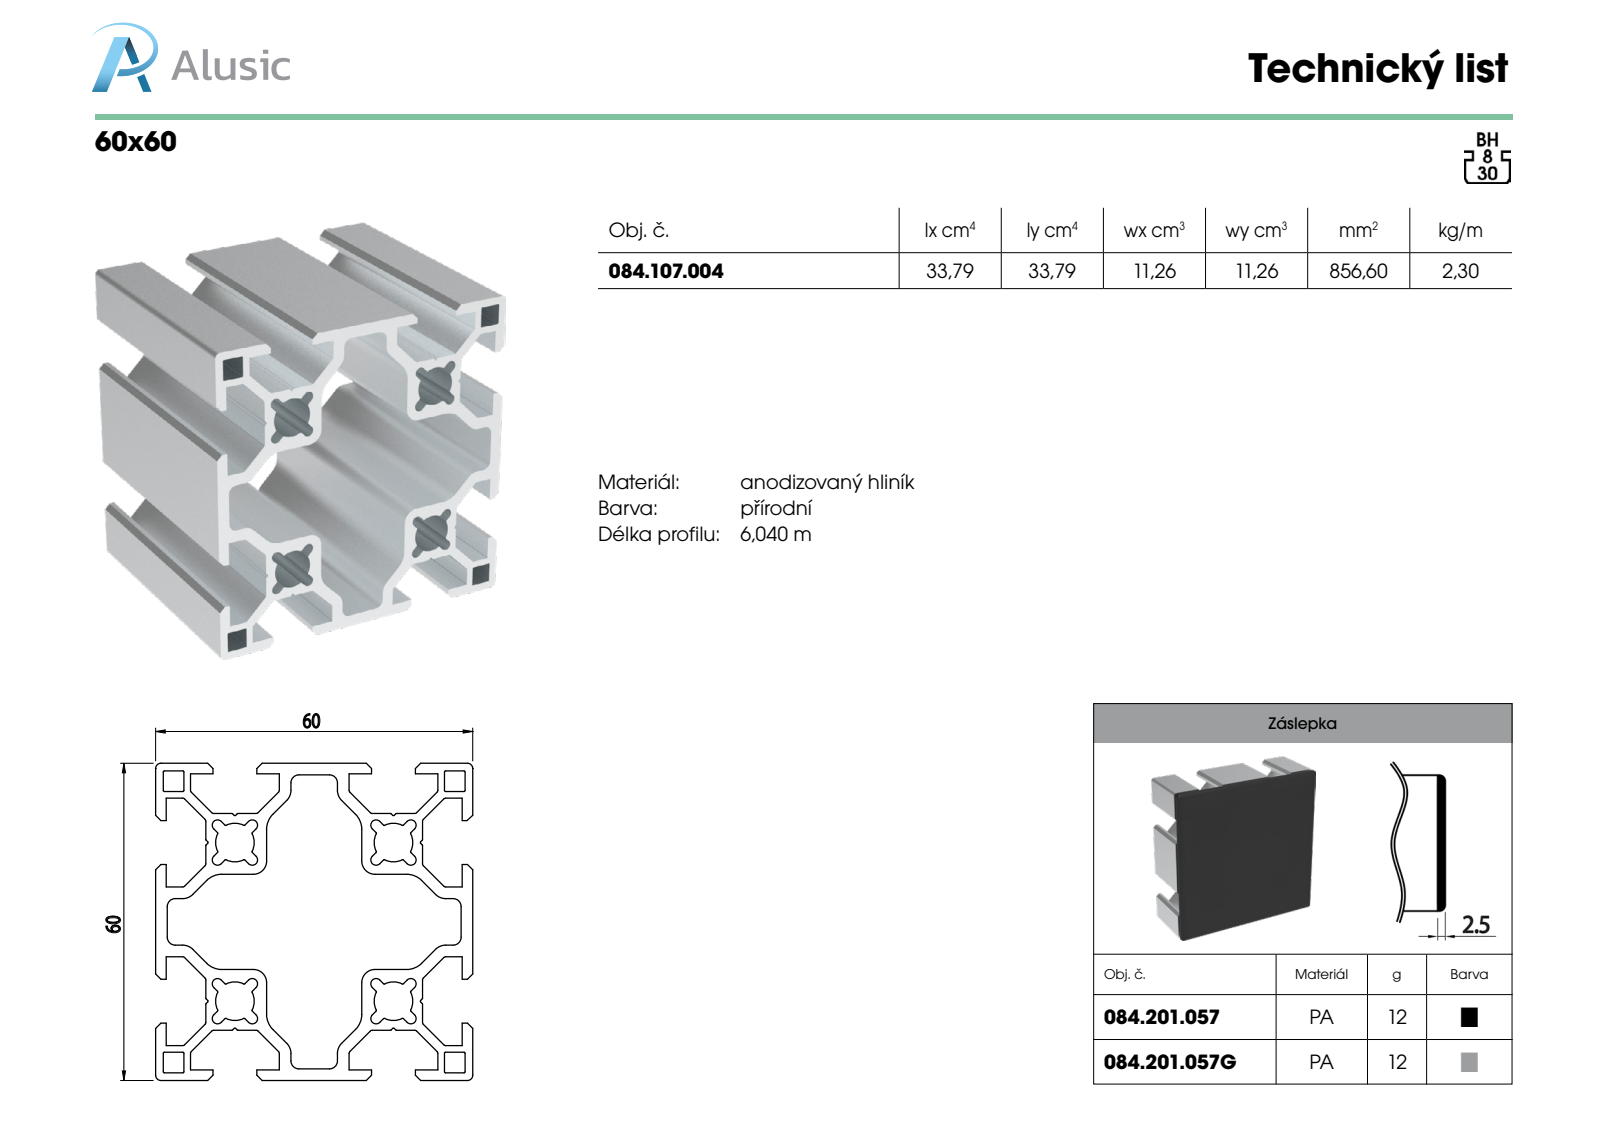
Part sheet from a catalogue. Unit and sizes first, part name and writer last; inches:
Units: inches
Overall size (bounding box): 2.362 × 2.362 × 0.295
Round holes (diameter × count): ⌀0.087 ×4
Round bosses / shafts (diameter × count): ⌀0.142 ×4
Partial cylindrical surfaces — rounded edges, fillets, slot ends (radius × count): R0.012 ×16, R0.039 ×4, R0.079 ×4, R0.144 ×2
Main face-to-face distances: 0.098, 1.795, 0.567, 0.614, 1.748, 0.047, 1.181, 2.362, 1.228, 1.134
Hole centre spacings: 2.094, 2.962
Volume: 0.553 in³ · Surface area: 12.64 in²
Bodies: 1 solid, 180 faces (84 planar, 58 cylindrical, 38 other)
Part name (STEP PRODUCT): 084.201.057
STEP written by: SolidWorks 2012 (CONFIG_CONTROL_DESIGN)
